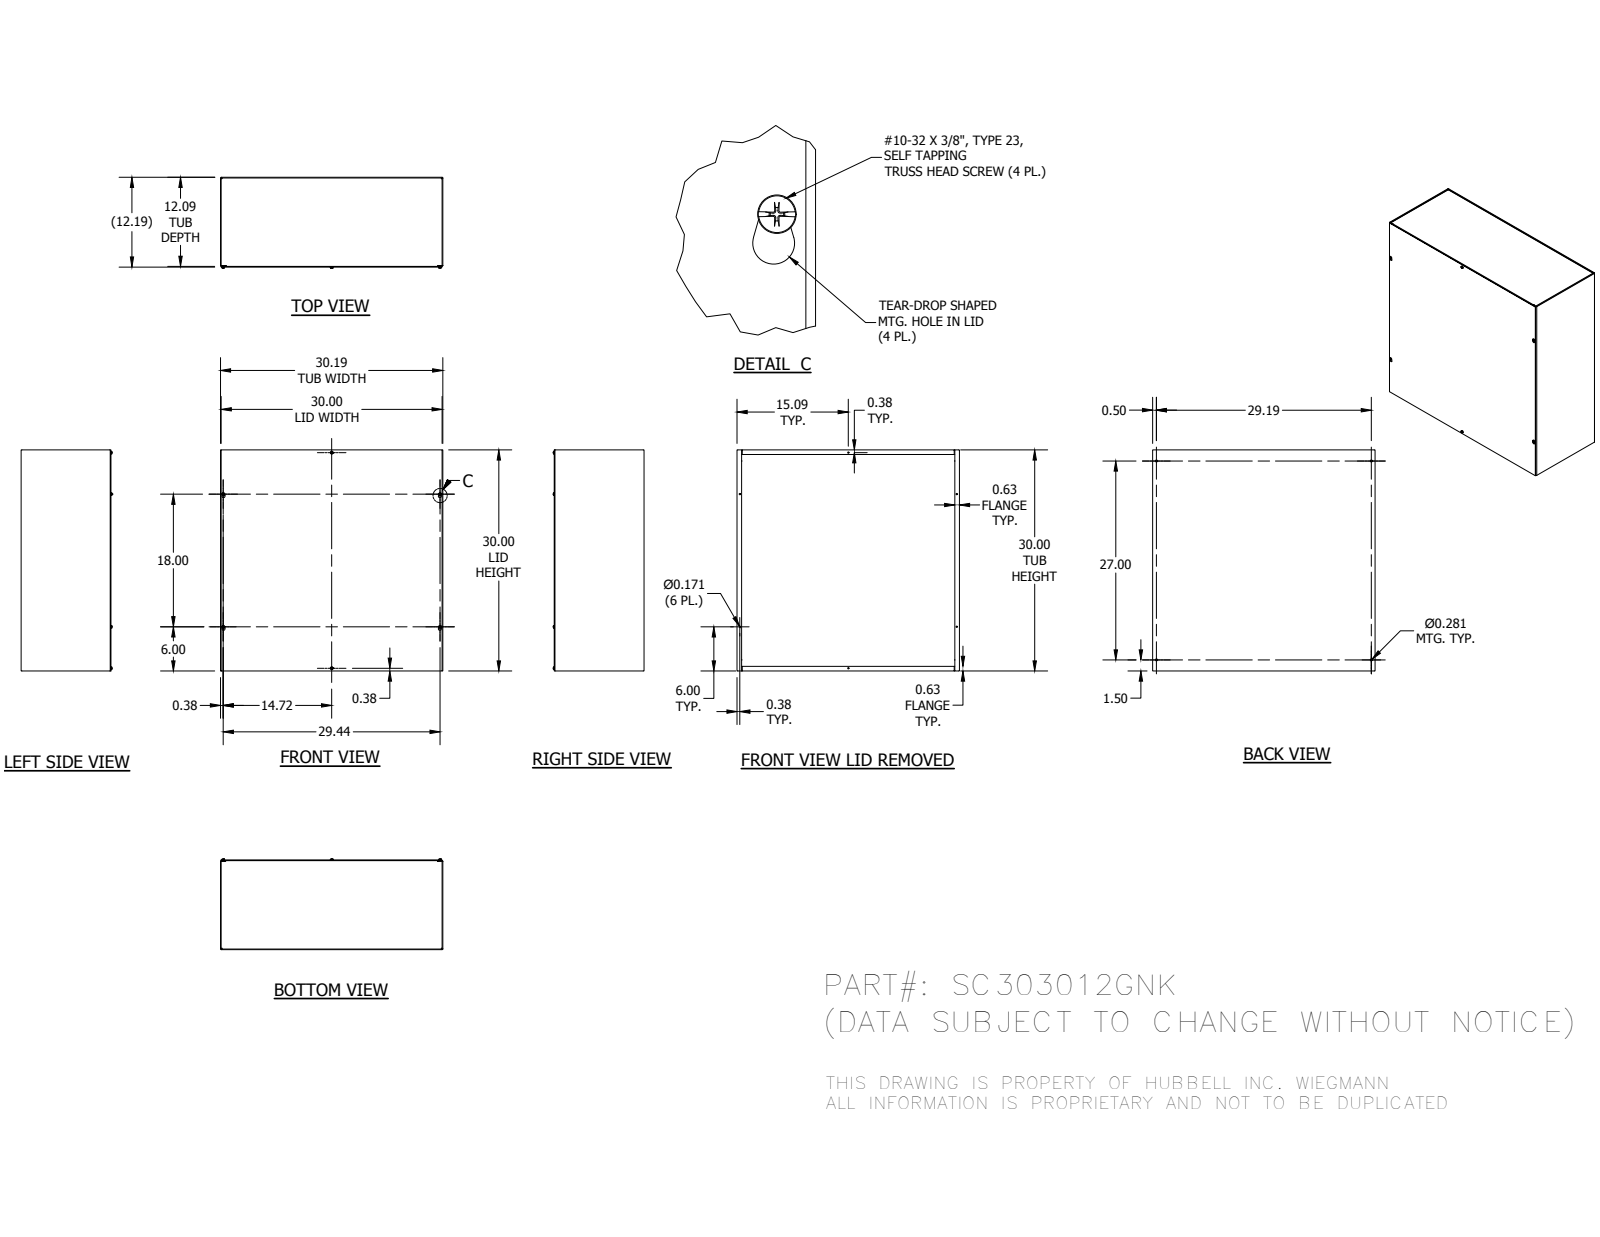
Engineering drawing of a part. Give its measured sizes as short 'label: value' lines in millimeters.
name: SC303012GNKBLR; SC3012GNKTB; SC3030GLPA; 37214 (+1 more)
written by: Autodesk Inventor 2014 (AUTOMOTIVE_DESIGN)
unit: mm
bodies: 10 solids, 404 faces (232 planar, 50 cylindrical, 122 other)
size: 766.76 × 762 × 312.91
volume: 5 157 000 mm³; area: 4 361 000 mm²
holes: 6× ⌀4.34, 4× ⌀7.14, 2× ⌀7.92
bosses: 6× ⌀4.83
rounds: 12× R0.4, 12× R2.78, 4× R3.17, 4× R5.16
face distances: 2.38, 307.18, 304.8, 309.56, 762, 759.62, 764.38, 757.24, 766.76, 4.76
hole spacings: 371.78, 400.23, 804.82, 114.34, 571.51, 707, 753.26, 938.59
